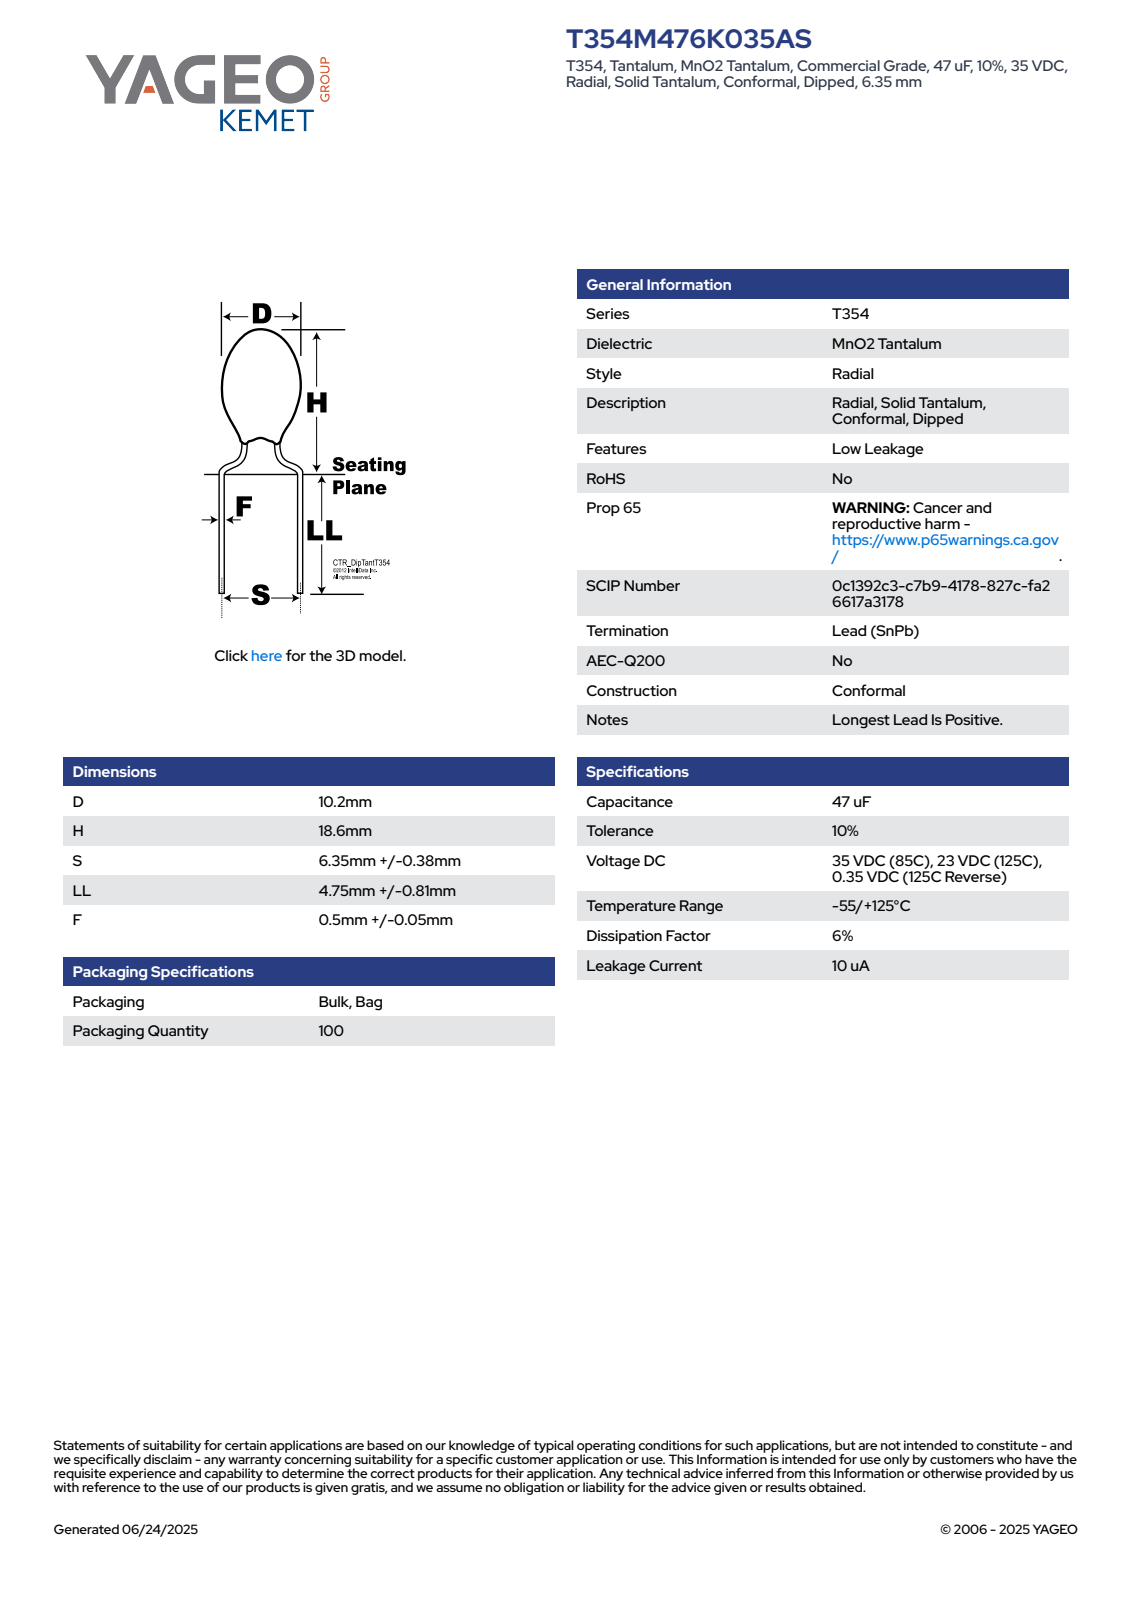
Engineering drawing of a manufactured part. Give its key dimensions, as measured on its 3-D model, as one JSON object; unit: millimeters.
{"part_name": "CTR_T354_D10.2H18.6S6.35LL5.56F0.55", "step_written_by": "SolidWorks 2014 (AUTOMOTIVE_DESIGN)", "units": "millimeters", "bodies": {"solids": 1, "faces": 81, "planar": 26, "cylindrical": 10, "other": 45}, "overall_size": [24.16, 10.2, 10.2], "volume_mm3": 891, "surface_area_mm2": 504, "round_bosses_or_shafts": [[0.55, 2], [10.2, 1]], "partial_cylinders_radius": [[5.09, 1]], "face_to_face_distances": [13.11, 11.05, 24.16, 19.66, 8.61, 4.5, 18.05, 7, 1.61, 6.11]}
